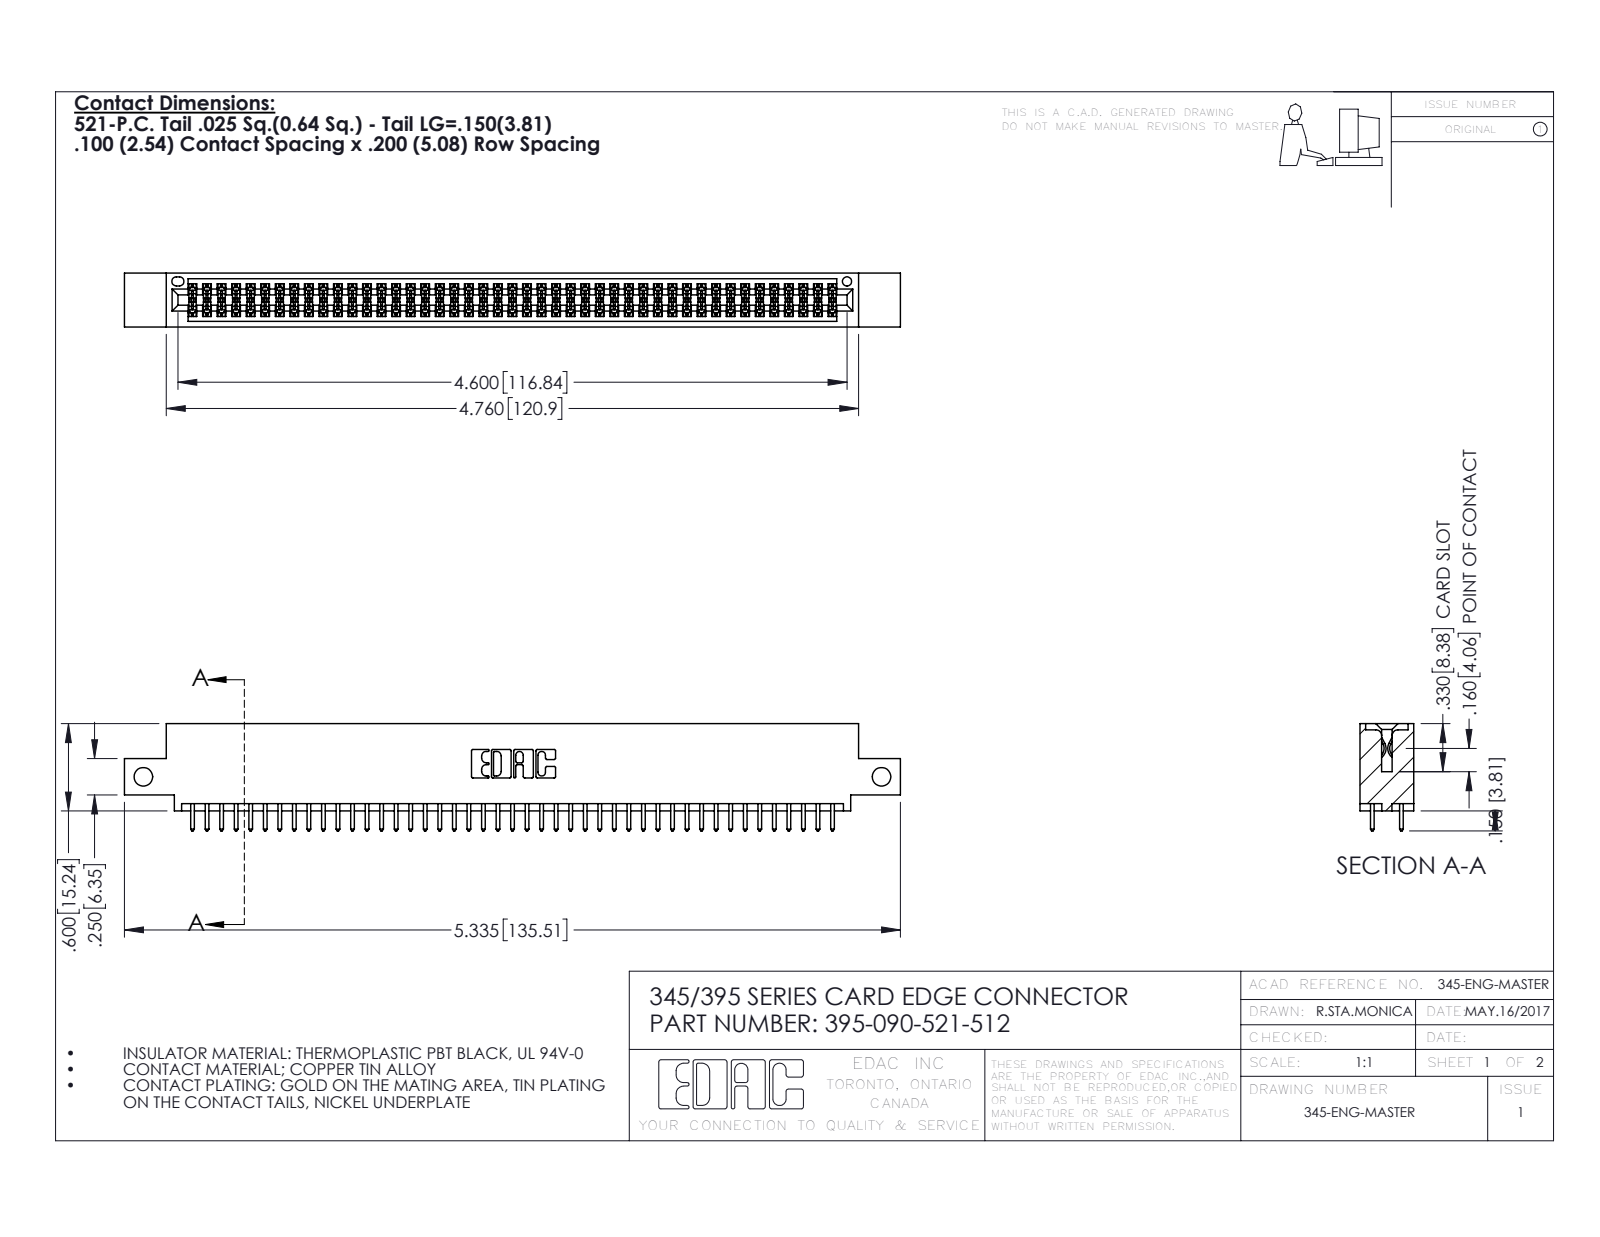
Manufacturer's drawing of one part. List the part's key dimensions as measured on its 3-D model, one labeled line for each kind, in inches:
Part name (STEP PRODUCT): 395-090-521-512; 345-292-001_345-293-121; 345 Part_0.110 Offset - Side Mount
STEP written by: SolidWorks 2016 (CONFIG_CONTROL_DESIGN)
Units: inches
Bodies: 91 solids, 4630 faces (3054 planar, 1576 cylindrical, 0 other)
Overall size (bounding box): 5.335 × 0.737 × 0.37
Volume: 0.793 in³ · Surface area: 29.42 in²
Round holes (diameter × count): ⌀0.128 ×2, ⌀0.064 ×1
Partial cylindrical surfaces — rounded edges, fillets, slot ends (radius × count): R0.006 ×135, R0.01 ×90, R0.01 ×22, R0.007 ×6, R0.031 ×6, R0.026 ×3, R0.014 ×2, R0.019 ×2
Main face-to-face distances: 0.298, 0.072, 0.2, 0.37, 0.098, 0.272, 0.025, 0.225, 0.175, 0.149
Hole centre spacings: 5.075
